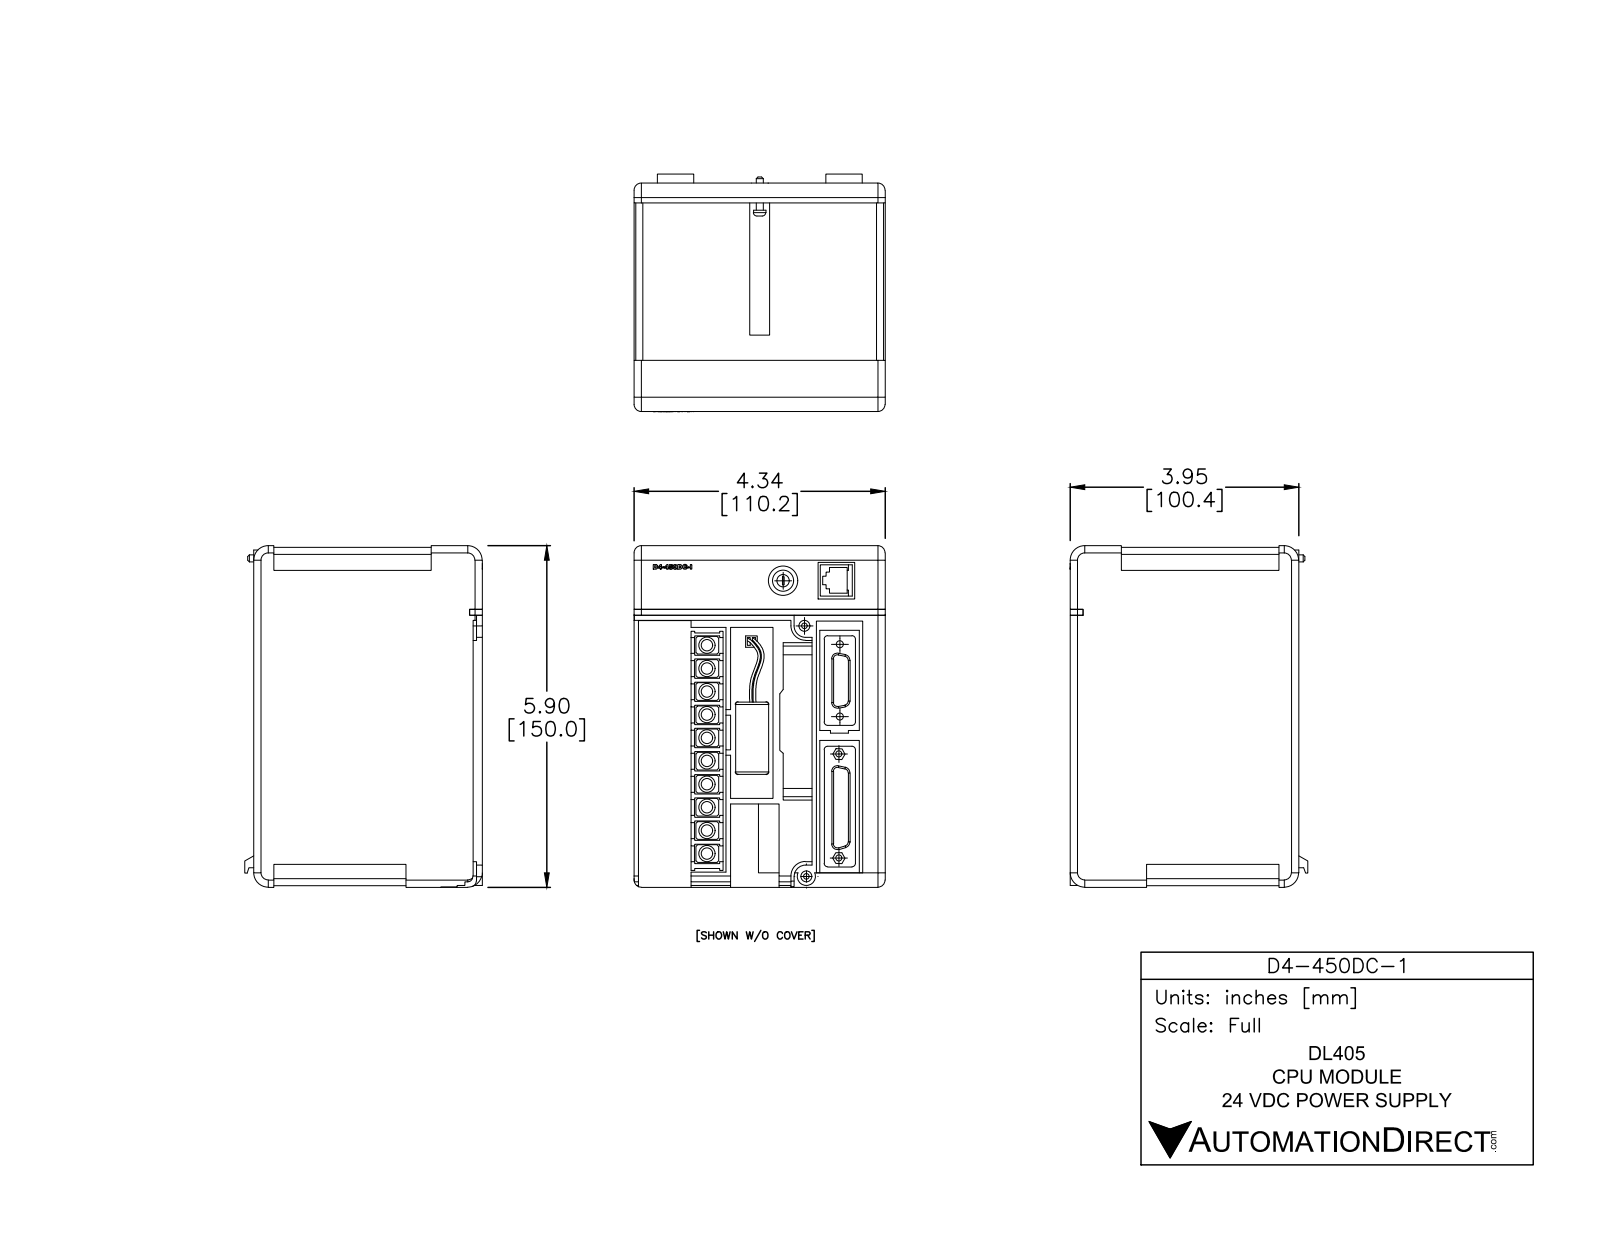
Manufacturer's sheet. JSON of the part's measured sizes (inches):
{"part_name": "D4-450DC-1", "step_written_by": "SolidWorks 2014 (AUTOMOTIVE_DESIGN)", "units": "inches", "bodies": {"solids": 3, "faces": 801, "planar": 609, "cylindrical": 110, "other": 82}, "overall_size": [5.905, 4.34, 4.106], "volume_in3": 89.68, "surface_area_in2": 180.4, "round_holes": [[0.1, 2], [0.12, 2], [0.104, 1], [0.105, 1], [0.188, 1], [0.188, 1], [0.216, 1], [0.51, 1]], "round_bosses_or_shafts": [[0.279, 10], [0.567, 1], [0.365, 1], [0.212, 1], [0.123, 1]], "partial_cylinders_radius": [[0.1, 9], [0.06, 8], [0.125, 8], [0.03, 6], [0.25, 6], [0.12, 4], [0.2, 2], [0.145, 1]], "face_to_face_distances": [4.34, 0.03, 5.845, 5.875, 3.95, 0.715, 3.235, 0.45, 0.115, 0.08], "hole_center_spacings": [0.644, 0.649, 0.69, 0.861, 1.248, 1.47, 1.681, 1.798]}
